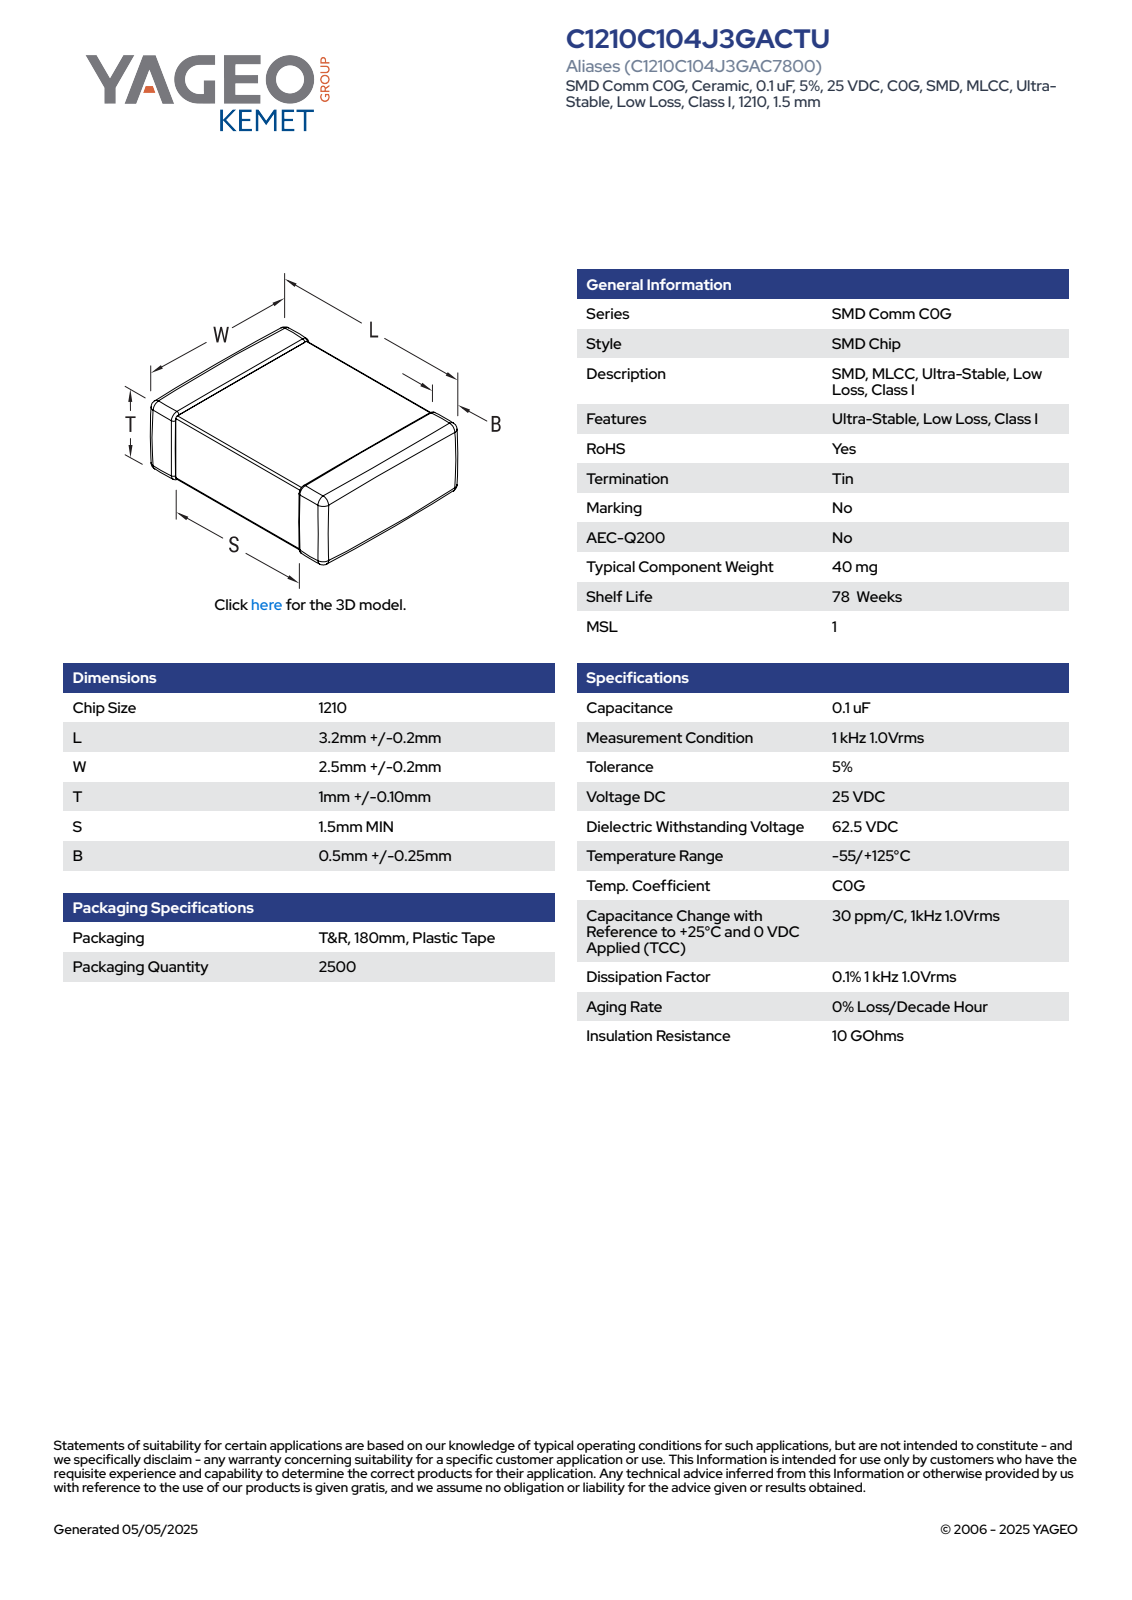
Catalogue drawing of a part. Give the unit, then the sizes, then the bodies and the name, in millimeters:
Units: millimetres
Overall size (bounding box): 3.4 × 2.7 × 1.1
Main face-to-face distances: 1.04, 0.98, 1.1, 3.4, 2.64, 2.58, 2.7, 1.05, 0.99, 1.31
Volume: 9 mm³ · Surface area: 31 mm²
Bodies: 4 solids, 125 faces (71 planar, 38 cylindrical, 16 other)
Part name (STEP PRODUCT): CCS_CCSTDNOS_1210_L3.4W2.7T1.1B0.75
STEP written by: SolidWorks 2014 (AUTOMOTIVE_DESIGN)
